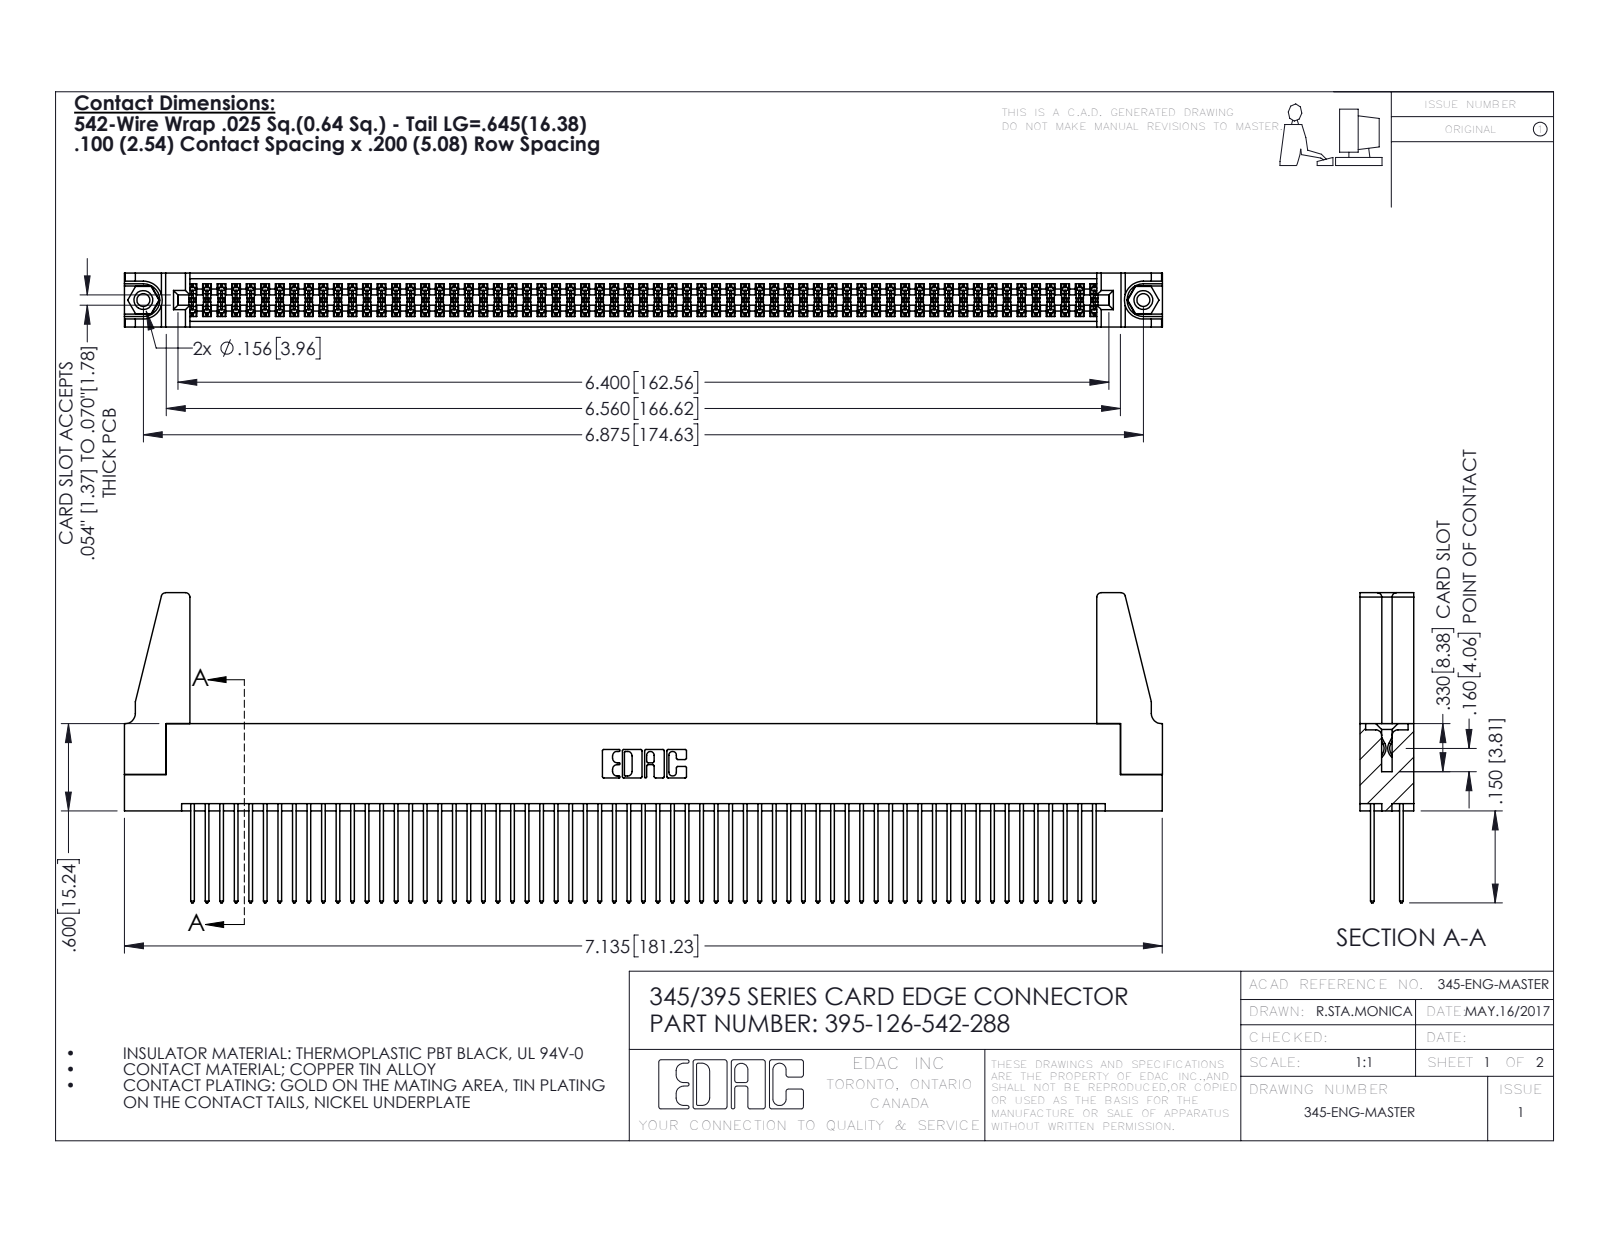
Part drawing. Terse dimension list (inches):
name: 345-220-078_345-220-088; 345-292-001_345-293-142; 395-126-542-288; 345-250-001_345-250-001-102 (+1 more)
written by: SolidWorks 2016 (CONFIG_CONTROL_DESIGN)
unit: in
bodies: 131 solids, 6550 faces (4310 planar, 2224 cylindrical, 16 other)
size: 7.136 × 2.132 × 0.37
volume: 1.321 in³; area: 51.86 in²
holes: 2× ⌀0.089, 2× ⌀0.125, 2× ⌀0.156, 1× ⌀0.064
bosses: 2× ⌀0.155
rounds: 189× R0.006, 126× R0.01, 22× R0.01, 8× R0.03, 6× R0.007, 6× R0.031, 3× R0.026, 2× R0.014
face distances: 0.072, 0.298, 0.2, 0.098, 0.272, 0.025, 0.37, 0.225, 0.175, 0.149
hole spacings: 0.27, 6.639, 6.875
